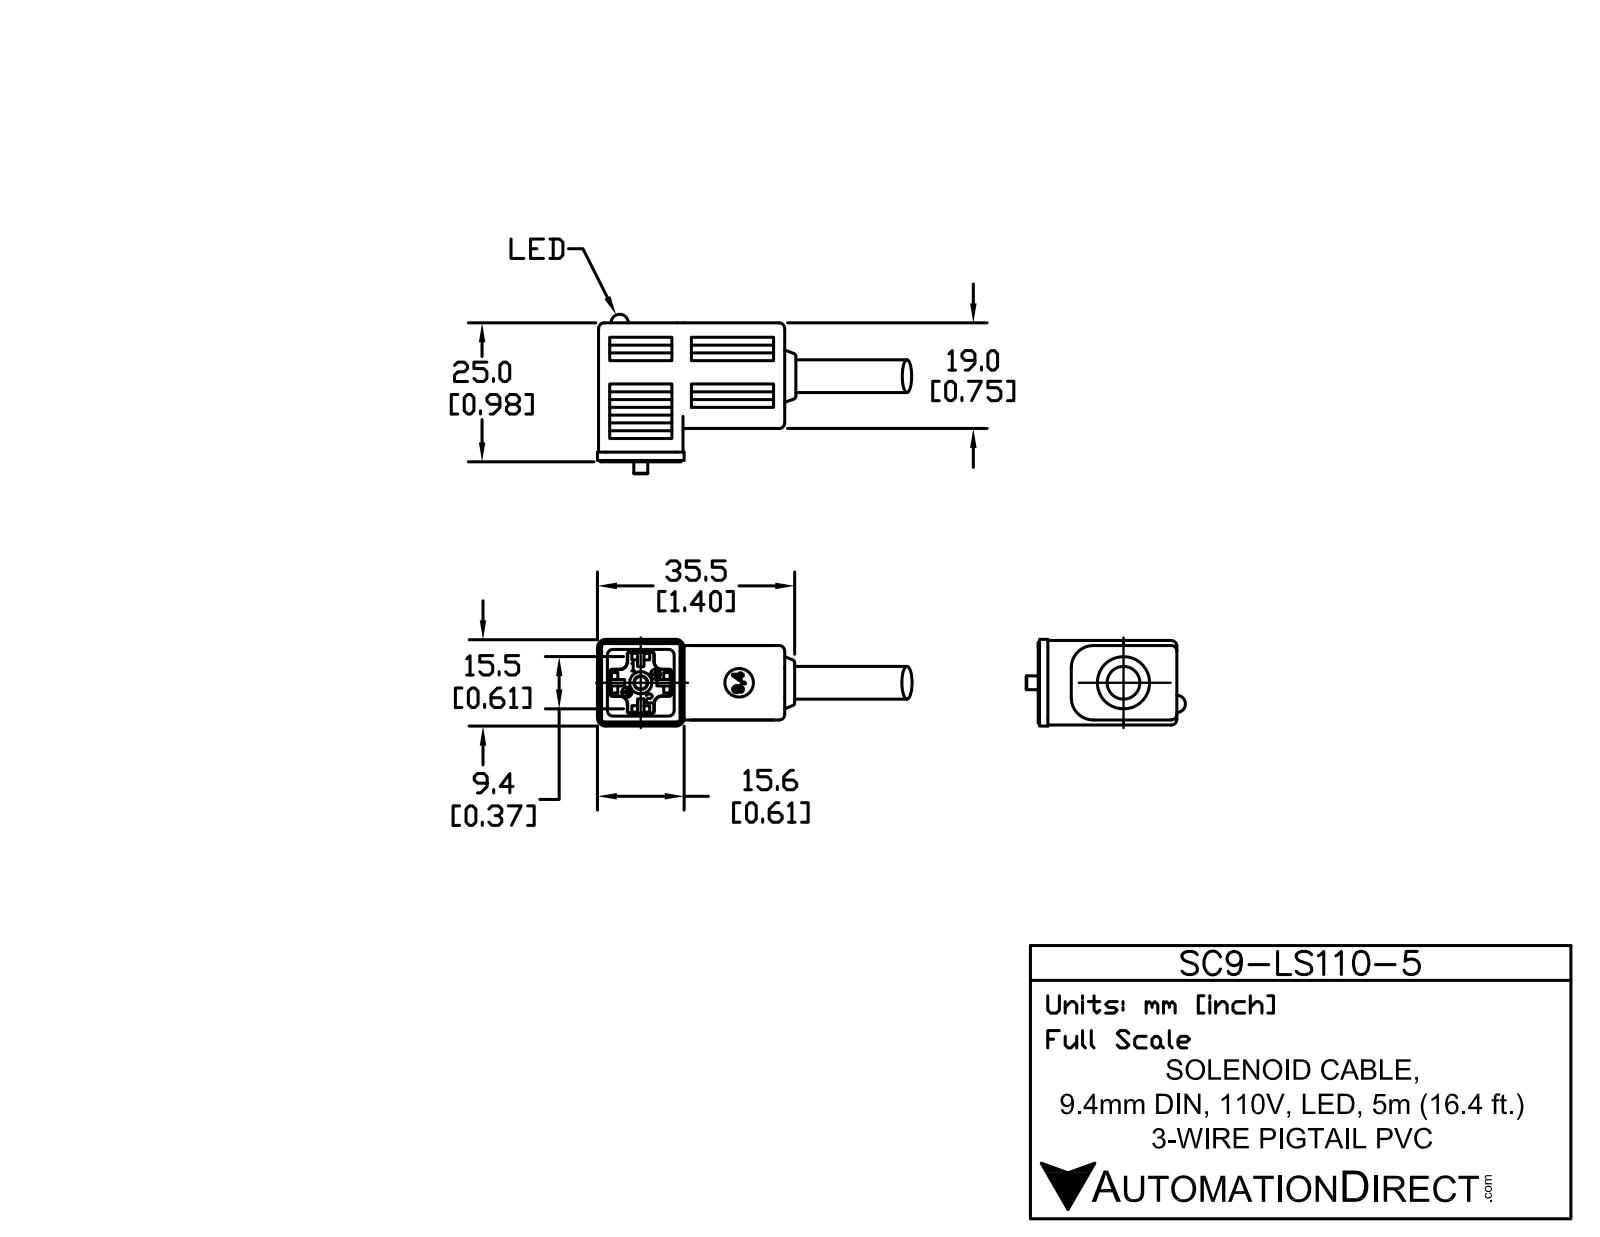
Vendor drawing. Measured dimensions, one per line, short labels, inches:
name: SC9-LS110-5
written by: SolidWorks 2011 (AUTOMOTIVE_DESIGN)
unit: in
bodies: 4 solids, 325 faces (256 planar, 37 cylindrical, 32 other)
size: 2.495 × 1.418 × 0.621
volume: 0.683 in³; area: 8.837 in²
holes: 2× ⌀0.089, 2× ⌀0.236, 1× ⌀0.157
bosses: 1× ⌀0.226, 1× ⌀0.118, 1× ⌀0.108
rounds: 10× R0.02, 4× R0.03, 4× R0.079, 3× R0.01, 2× R0.157
face distances: 0.876, 0.035, 0.039, 0.61, 0.564, 0.915, 0.541, 0.034, 0.576, 0.576
hole spacings: 0.13, 0.141, 0.256
